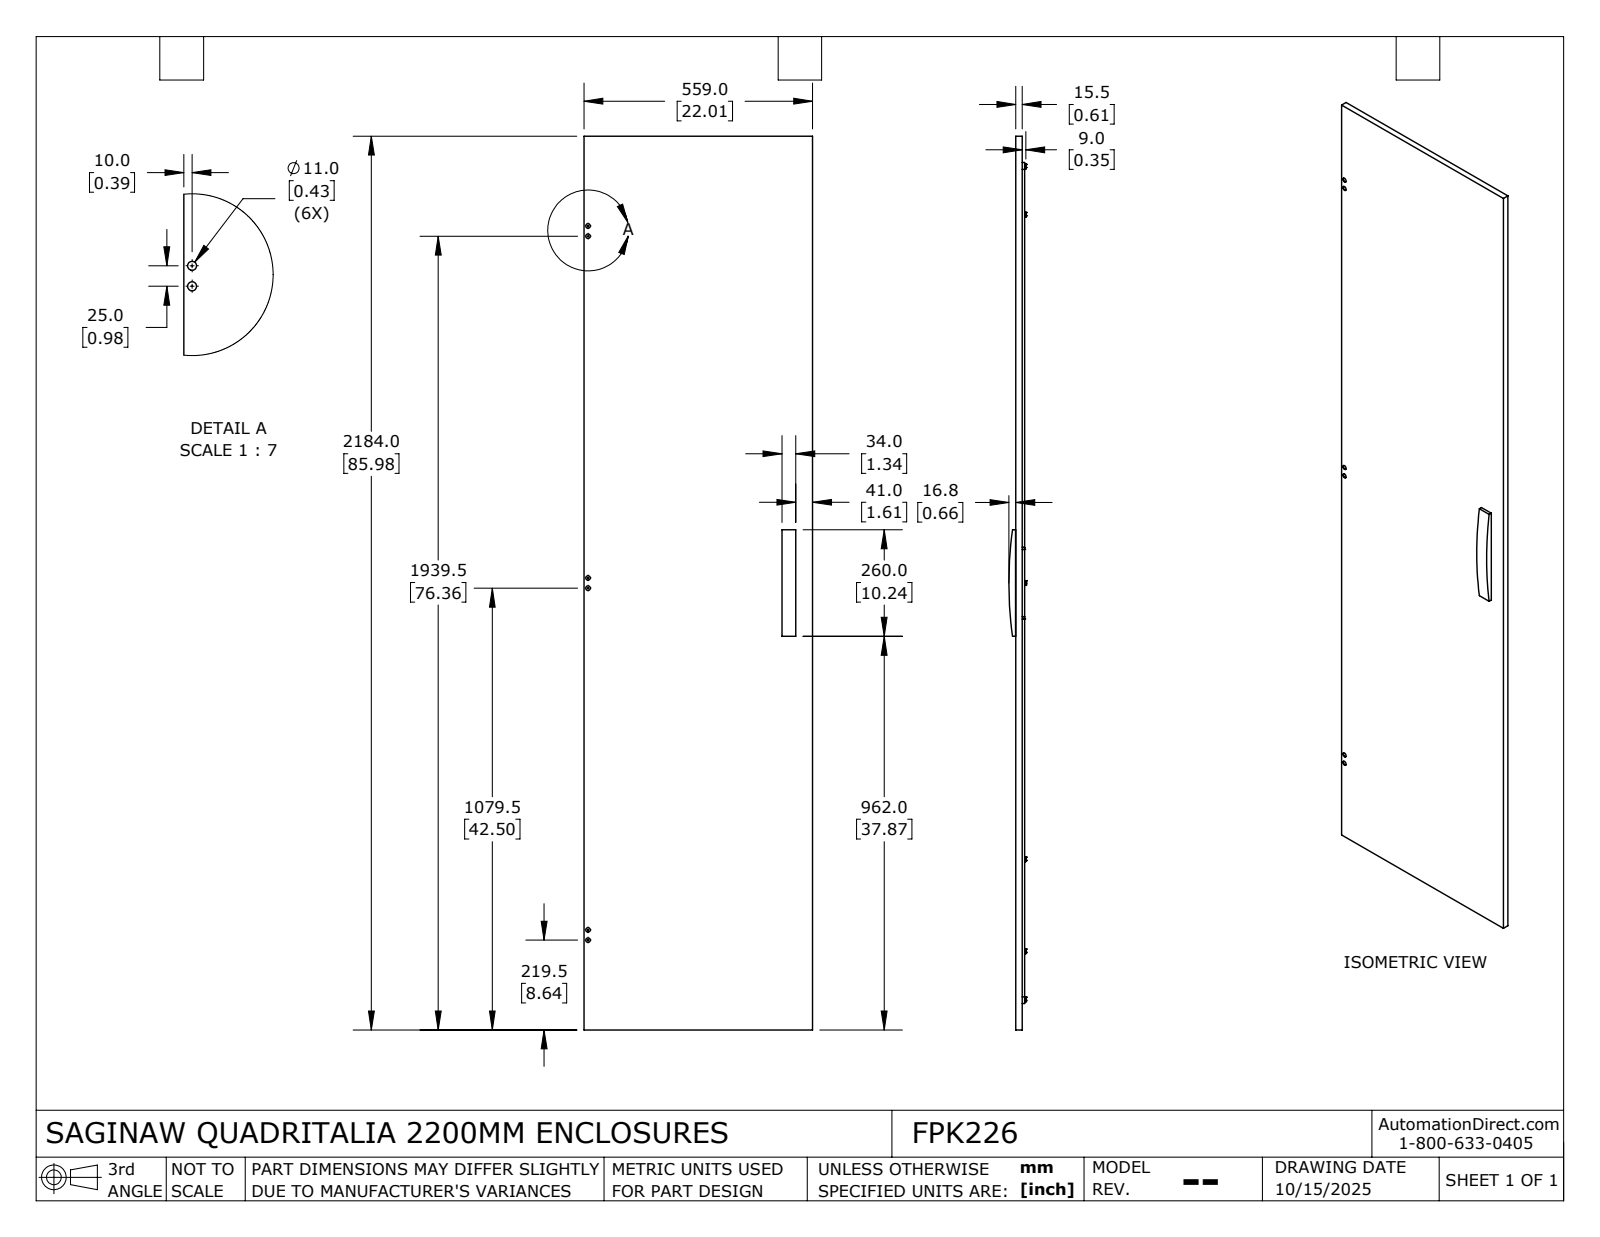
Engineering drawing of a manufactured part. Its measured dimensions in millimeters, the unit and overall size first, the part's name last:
Units: millimetres
Overall size (bounding box): 2184 × 559 × 41.32
Round holes (diameter × count): ⌀4.25 ×152, ⌀9 ×13, ⌀4.92 ×8, ⌀11 ×6
Round bosses / shafts (diameter × count): ⌀7 ×5, ⌀6 ×5, ⌀7.2 ×1
Partial cylindrical surfaces — rounded edges, fillets, slot ends (radius × count): R5.77 ×8, R7.52 ×4, R962.86 ×1
Main face-to-face distances: 1.5, 20, 21.5, 360, 557.5, 380, 340, 75, 484, 73.5
Hole centre spacings: 25, 50, 75, 100, 125, 150, 175, 200
Volume: 4 342 000 mm³ · Surface area: 2 906 000 mm²
Bodies: 2 solids, 632 faces (303 planar, 227 cylindrical, 102 other)
Part name (STEP PRODUCT): FPK226
STEP written by: SolidWorks 2024 (AUTOMOTIVE_DESIGN)
